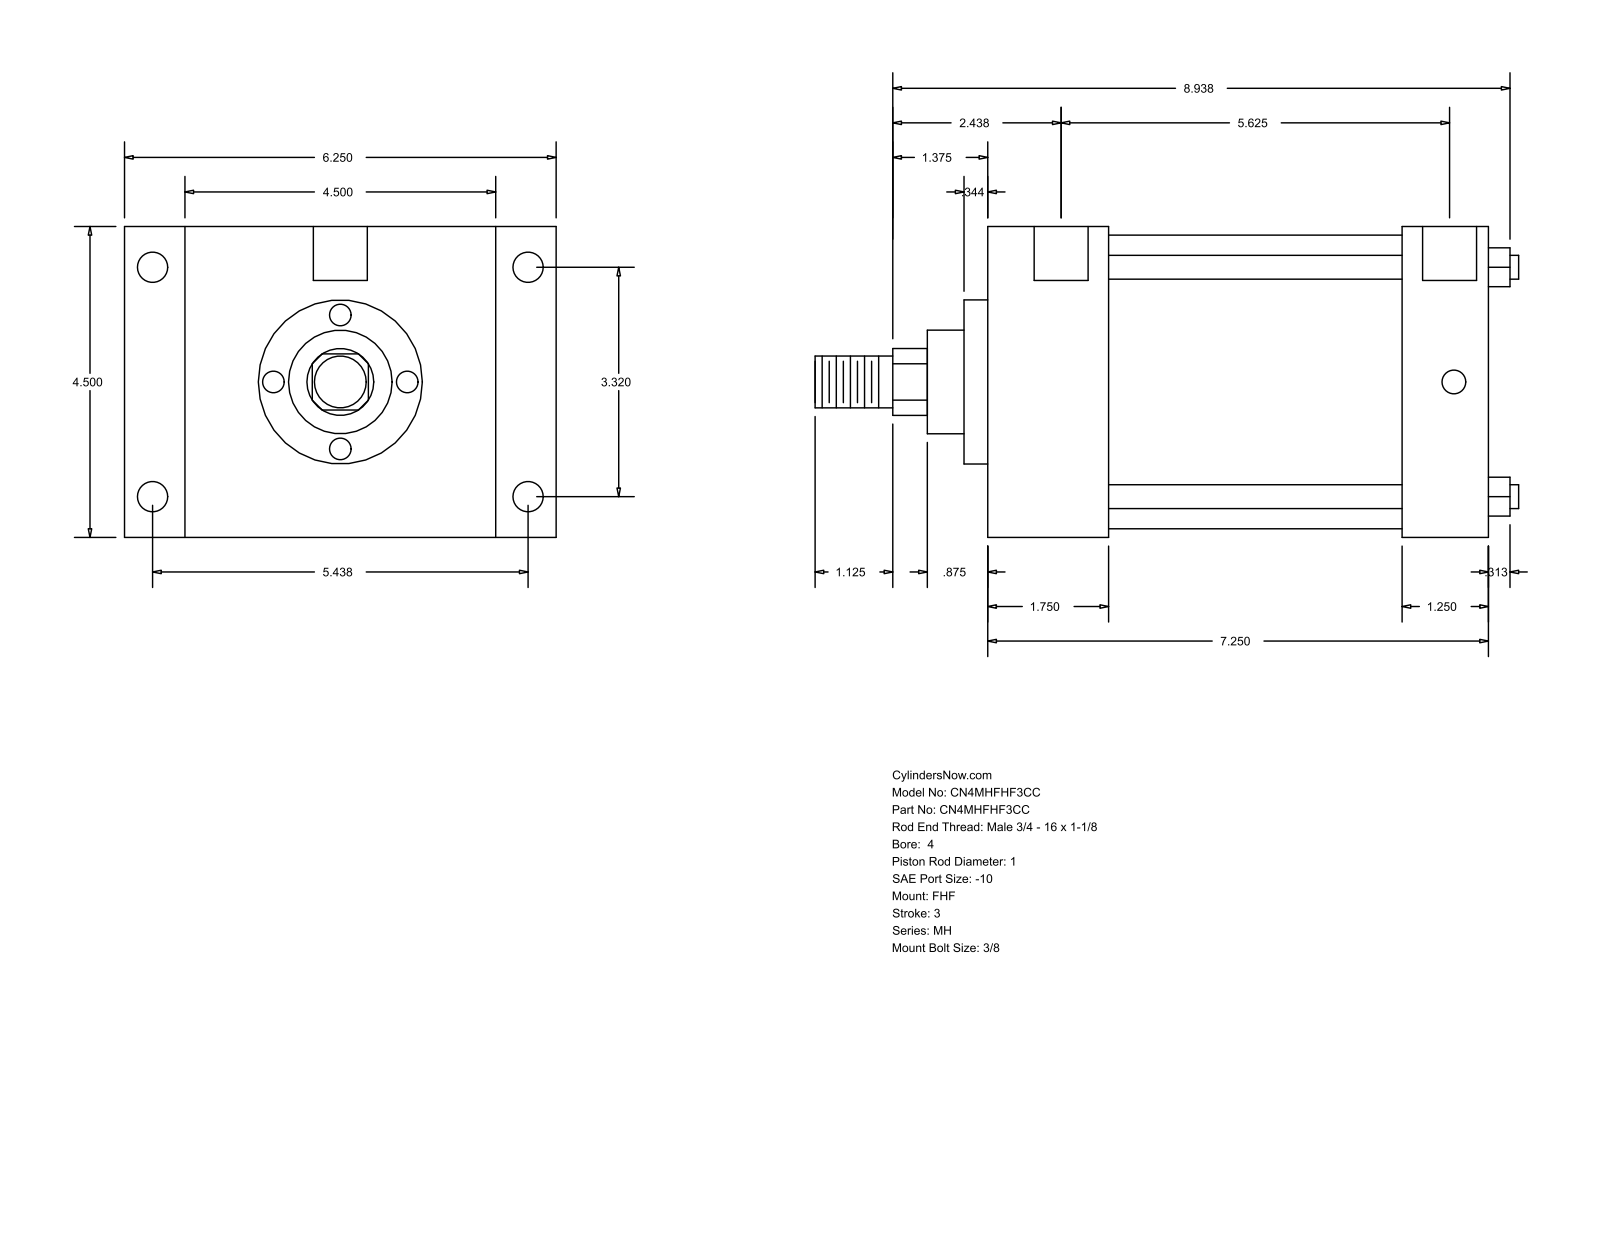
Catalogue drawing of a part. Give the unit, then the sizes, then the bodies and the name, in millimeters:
Units: millimetres
Overall size (bounding box): 258.76 × 158.75 × 114.3
Round holes (diameter × count): ⌀8.73 ×4, ⌀11.13 ×4, ⌀19.84 ×2
Round bosses / shafts (diameter × count): ⌀8.76 ×4, ⌀107.95 ×1, ⌀60.33 ×1, ⌀38.1 ×1, ⌀25.4 ×1, ⌀19.05 ×1
Partial cylindrical surfaces — rounded edges, fillets, slot ends (radius × count): R12.29 ×1
Main face-to-face distances: 114.3, 184.15, 44.46, 139.69, 22.23, 136.53, 158.76, 152.4, 107.94, 31.75
Hole centre spacings: 84.32, 138.12, 146.05, 161.82, 1.58, 1.59, 142.88, 144.46
Bodies: 0 solids, 90 faces (61 planar, 29 cylindrical, 0 other)
Part name (STEP PRODUCT): MH_FHF__0400_1
STEP written by: GSSL Pune (CONFIG_CONTROL_DESIGN)
